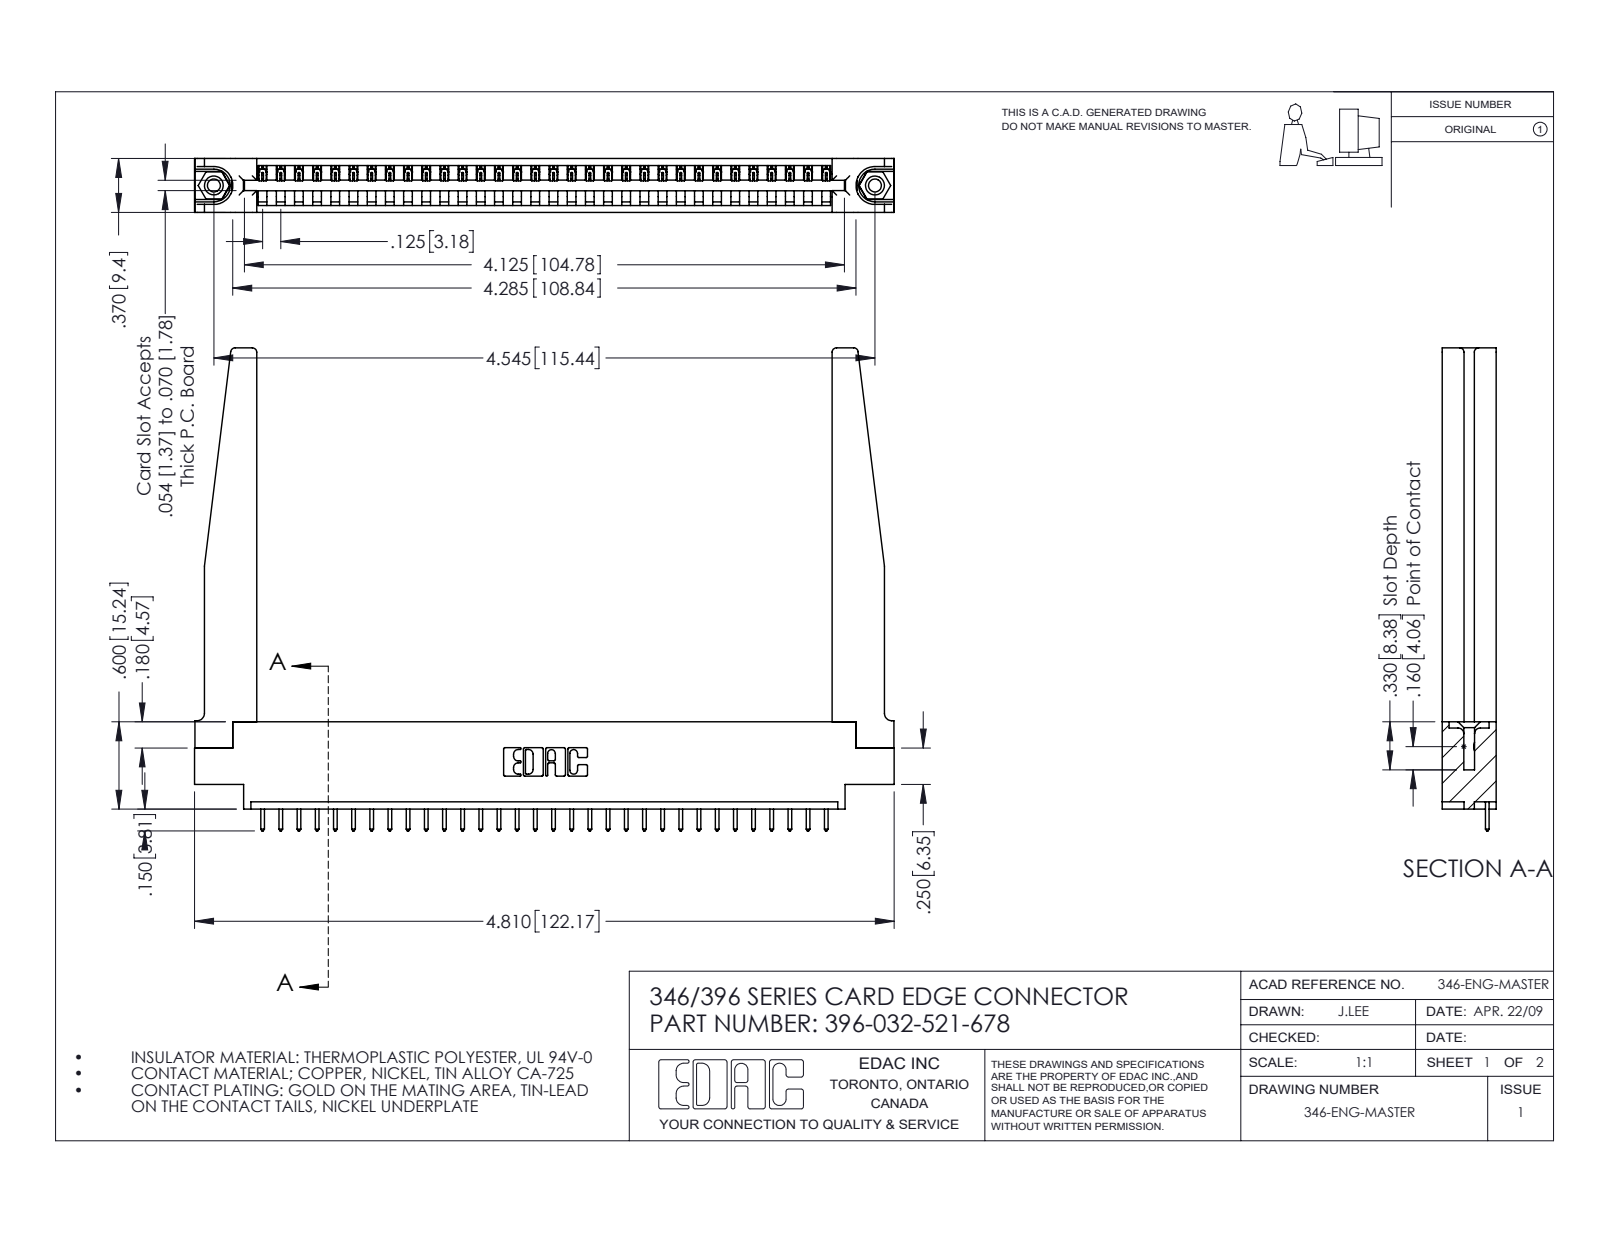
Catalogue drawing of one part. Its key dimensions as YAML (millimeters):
part_name: "345-292-001_345-293-121; 346 Part_0.170 Offset - 0.156 Dia-TH; 346-220-078_345-220-078; 396-032-521-678 (+1 more)"
step_written_by: "SolidWorks 2016 (CONFIG_CONTROL_DESIGN)"
units: millimeters
bodies: {solids: 37, faces: 2216, planar: 1502, cylindrical: 662, other: 52}
overall_size: [122.2, 84.3, 9.4]
volume: 18290
surface_area: 20450
round_holes:
  - {diameter: 2.3, count: 2}
  - {diameter: 3.2, count: 2}
  - {diameter: 4, count: 2}
  - {diameter: 1.6, count: 1}
round_bosses_or_shafts:
  - {diameter: 3.9, count: 2}
partial_cylinders:
  - {radius: 0.2, count: 64}
  - {radius: 0.3, count: 64}
  - {radius: 0.3, count: 22}
  - {radius: 0.8, count: 8}
  - {radius: 0.2, count: 6}
  - {radius: 0.8, count: 6}
  - {radius: 0.7, count: 3}
  - {radius: 0.8, count: 2}
face_to_face_distances: [9.4, 1.2, 8.2, 1.8, 3.8, 3.8, 6.4, 7.6, 0.6, 5.6]
hole_center_spacings: [6.2, 110.2, 115.4]
